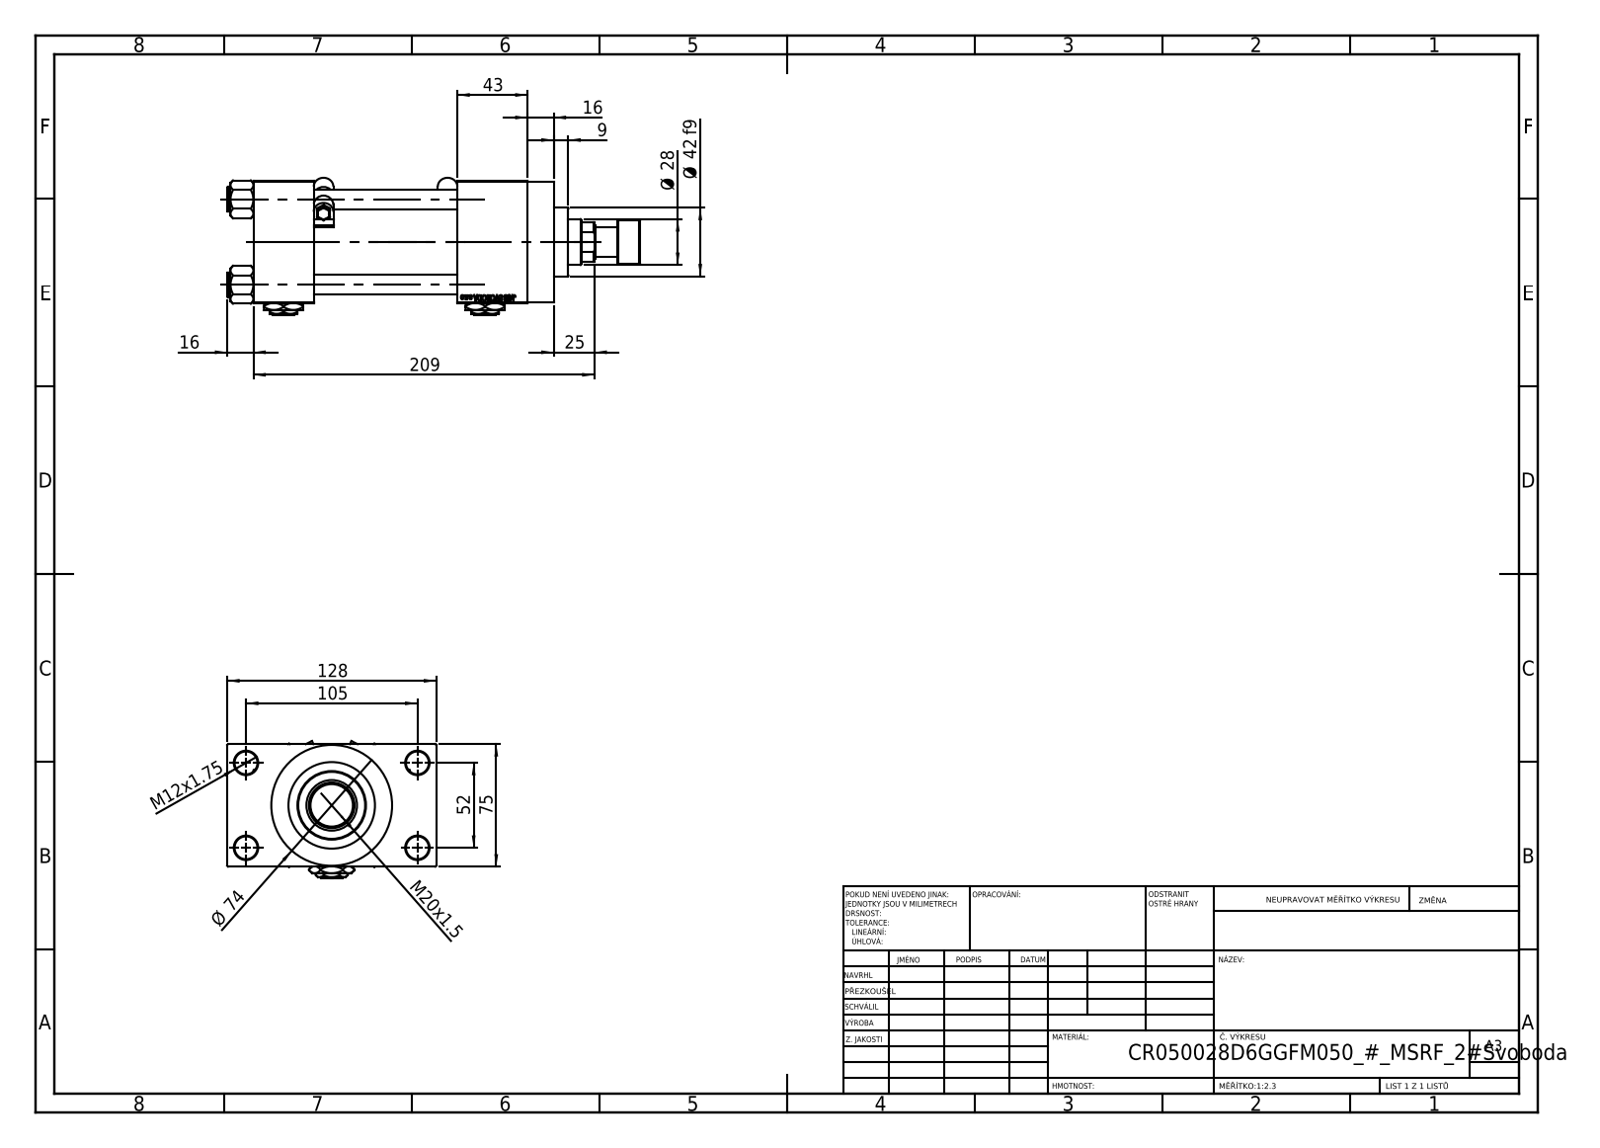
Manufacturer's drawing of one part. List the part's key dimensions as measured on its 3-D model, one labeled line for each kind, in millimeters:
Part name (STEP PRODUCT): V215_VC_A; V215CR_ROD_END_F; NUT_M5_D; V215CR_VCP_D (+4 more)
STEP written by: SolidWorks 2019 (CONFIG_CONTROL_DESIGN)
Units: millimetres
Bodies: 16 solids, 1283 faces (585 planar, 132 cylindrical, 566 other)
Overall size (bounding box): 253 × 128 × 83.88
Volume: 876 881 mm³ · Surface area: 198 008 mm²
Round holes (diameter × count): ⌀12 ×4, ⌀14 ×4, ⌀7 ×2, ⌀20.96 ×2, ⌀30 ×2, ⌀18.5 ×1, ⌀28 ×1, ⌀31 ×1, ⌀41 ×1, ⌀50 ×1, ⌀53 ×1
Round bosses / shafts (diameter × count): ⌀15 ×4, ⌀5 ×2, ⌀2.5 ×2, ⌀74 ×1, ⌀56 ×1, ⌀42 ×1, ⌀27 ×1, ⌀18 ×1
Partial cylindrical surfaces — rounded edges, fillets, slot ends (radius × count): R0.5 ×12, R6 ×4
Main face-to-face distances: 75, 88, 37, 125, 26.5, 101.5, 168, 131, 43, 16
Hole centre spacings: 26.35, 36.98, 52.3, 58.43, 58.59, 78.65, 94.37, 52
